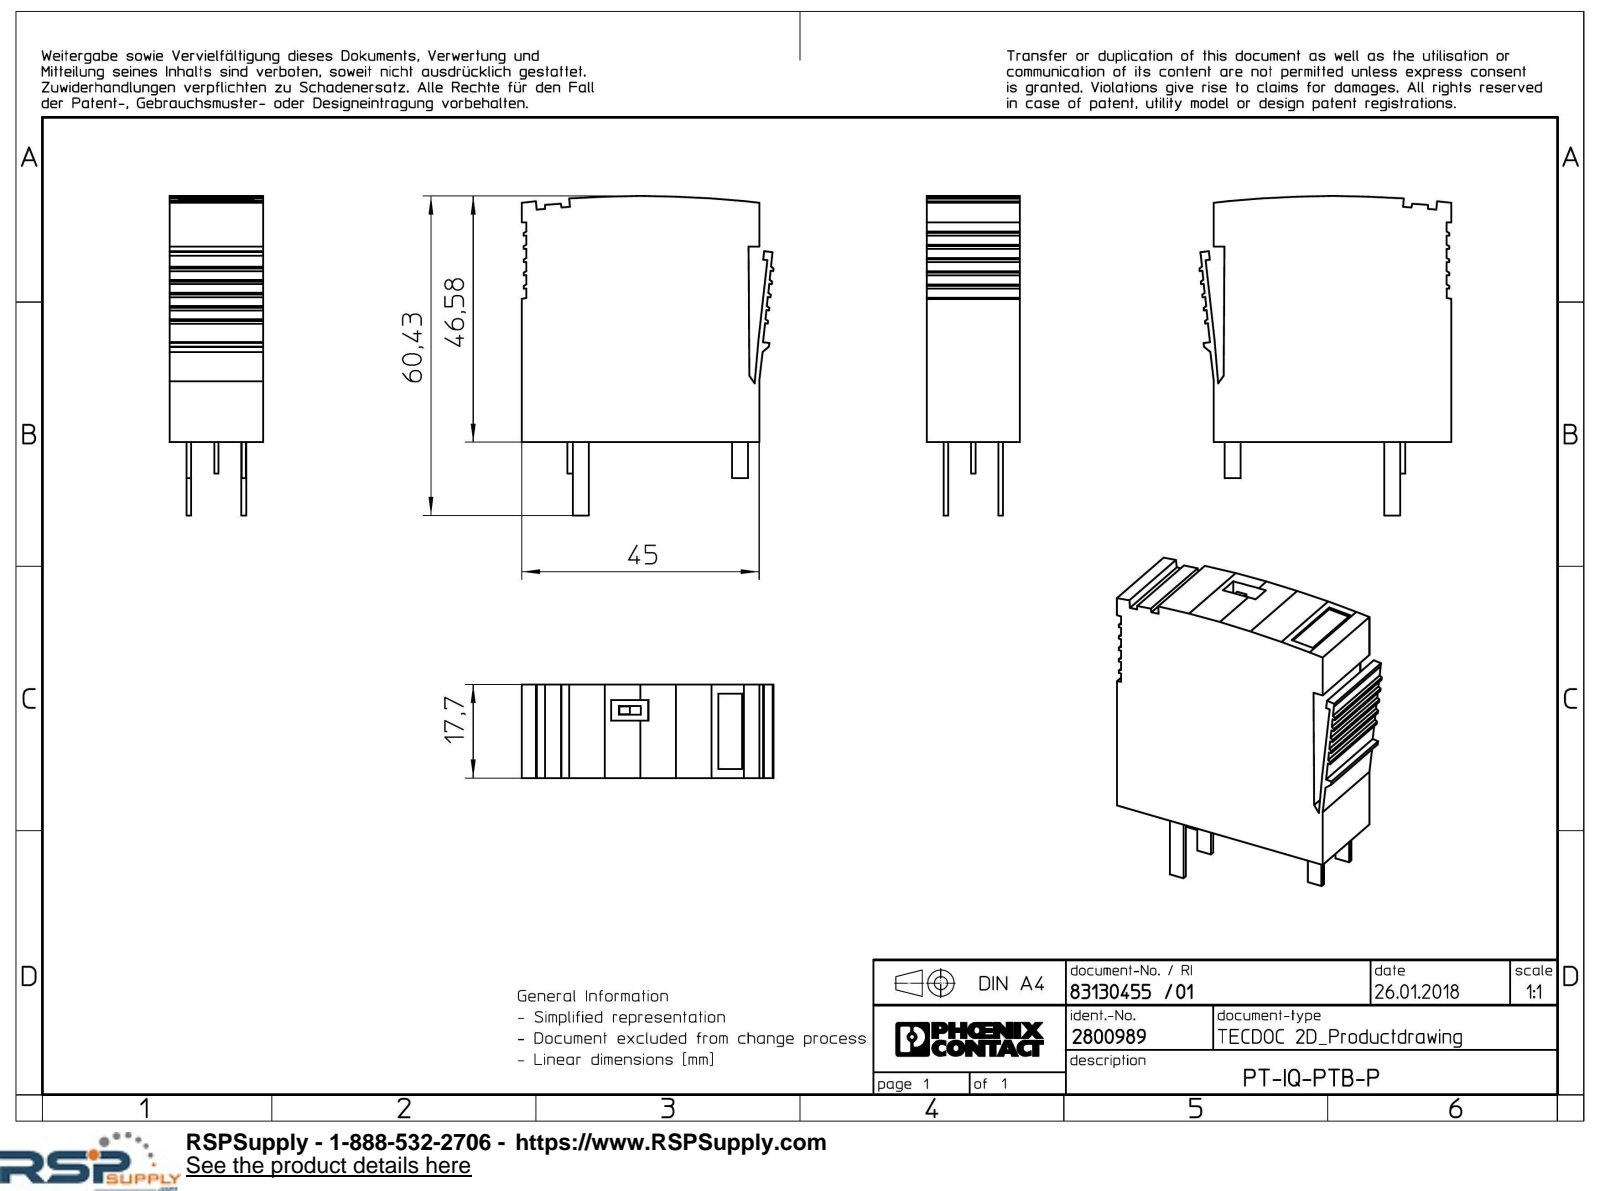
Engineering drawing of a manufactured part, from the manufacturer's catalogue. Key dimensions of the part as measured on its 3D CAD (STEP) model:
Part name (STEP PRODUCT): PT_IQ_PTB_P-select
STEP written by: Creo Elements/Direct Modeling 20.1A 29-Sep-2018 (C) Parametric Technology GmbH (AUTOMOTIVE_DESIGN)
Units: millimetres
Bodies: 1 solid, 169 faces (159 planar, 6 cylindrical, 4 other)
Overall size (bounding box): 60.42 × 47.71 × 17.7
Volume: 34 993 mm³ · Surface area: 9 612 mm²
Partial cylindrical surfaces — rounded edges, fillets, slot ends (radius × count): R0.3 ×4, R1.48 ×2
Main face-to-face distances: 17.7, 45, 0.9, 44.1, 1.1, 2.5, 1.85, 8.55, 10.4, 1
